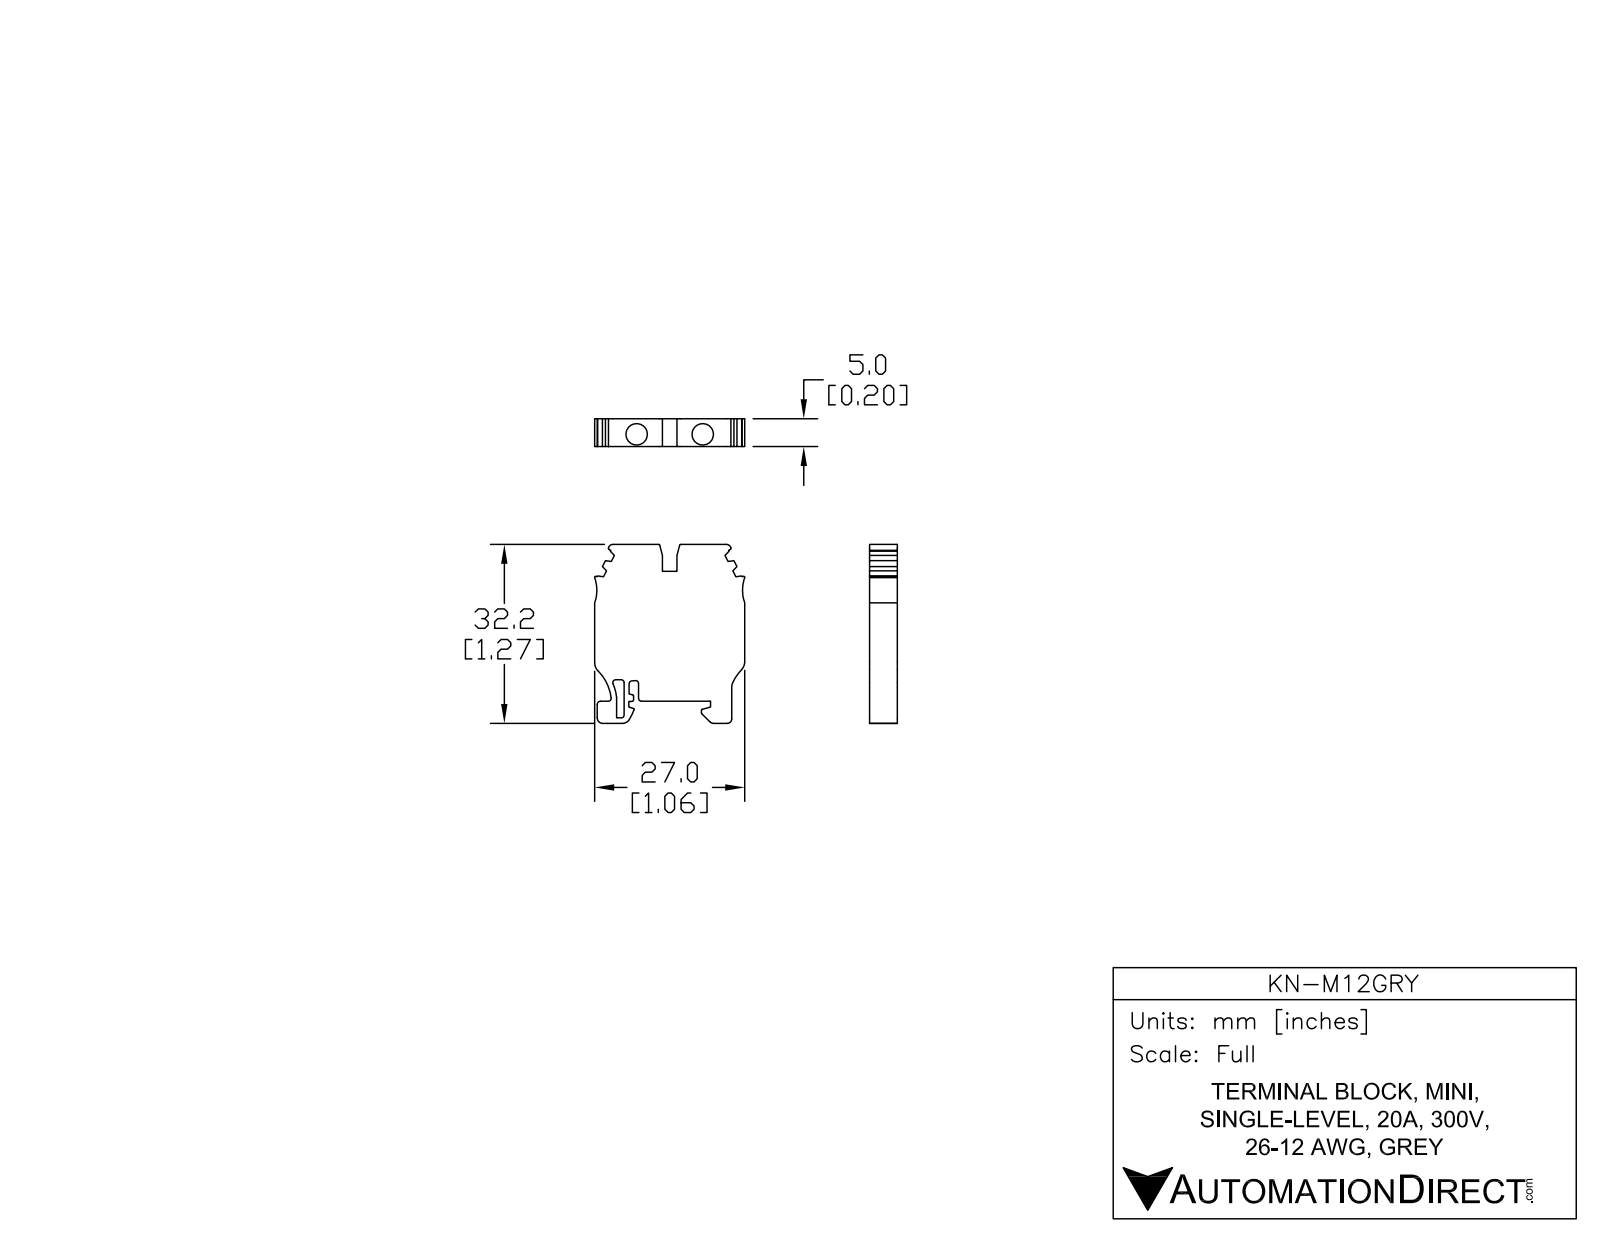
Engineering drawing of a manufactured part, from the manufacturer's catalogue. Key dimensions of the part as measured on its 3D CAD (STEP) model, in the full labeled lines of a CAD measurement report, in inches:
Part name (STEP PRODUCT): KN-M12GRY
STEP written by: SolidWorks 2014 (AUTOMOTIVE_DESIGN)
Units: inches
Bodies: 1 solid, 104 faces (64 planar, 40 cylindrical, 0 other)
Overall size (bounding box): 1.268 × 1.063 × 0.197
Volume: 0.214 in³ · Surface area: 3.658 in²
Round holes (diameter × count): ⌀0.152 ×2
Partial cylindrical surfaces — rounded edges, fillets, slot ends (radius × count): R0.008 ×9, R0.02 ×7, R0.031 ×4, R0.079 ×3, R0.273 ×2, R0.012 ×1, R0.024 ×1, R0.039 ×1
Main face-to-face distances: 0.197, 1.11, 0.157, 1.063, 0.156, 1.268, 0.209, 0.854, 0.971, 0.763
Hole centre spacings: 0.469
